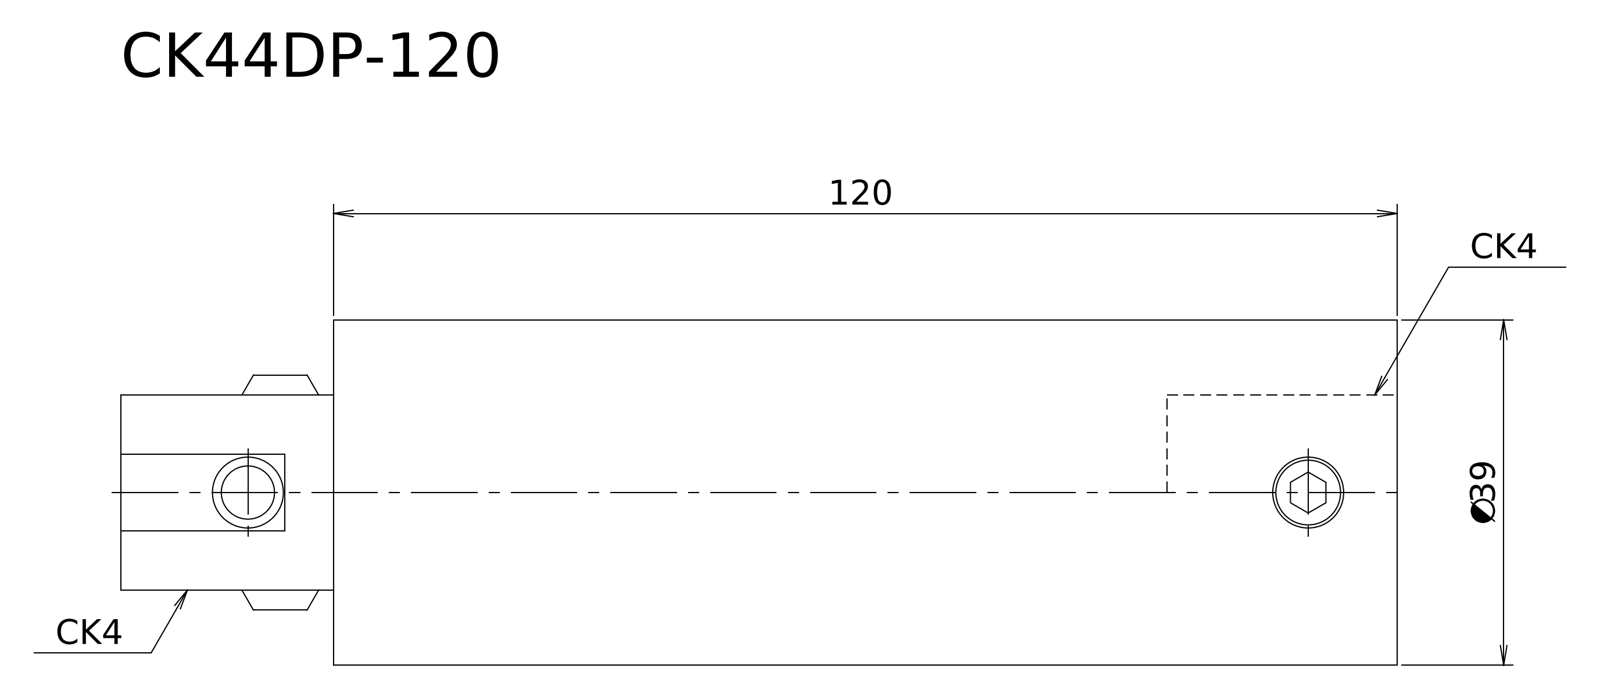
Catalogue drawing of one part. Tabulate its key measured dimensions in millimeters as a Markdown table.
| quantity | value |
| --- | --- |
| STEP written by | Kubotek KeyCreator V8.5.1 (14335) (CONFIG_CONTROL_DESIGN) |
| units | millimeters |
| bodies | 1 solid, 3 faces (2 planar, 1 cylindrical, 0 other) |
| overall size | 120 × 39 × 39 |
| volume | 143 351 mm³ |
| surface area | 17 092 mm² |
| round bosses / shafts (diameter × count) | 39 × 1 |
| main face-to-face distances | 120 |
